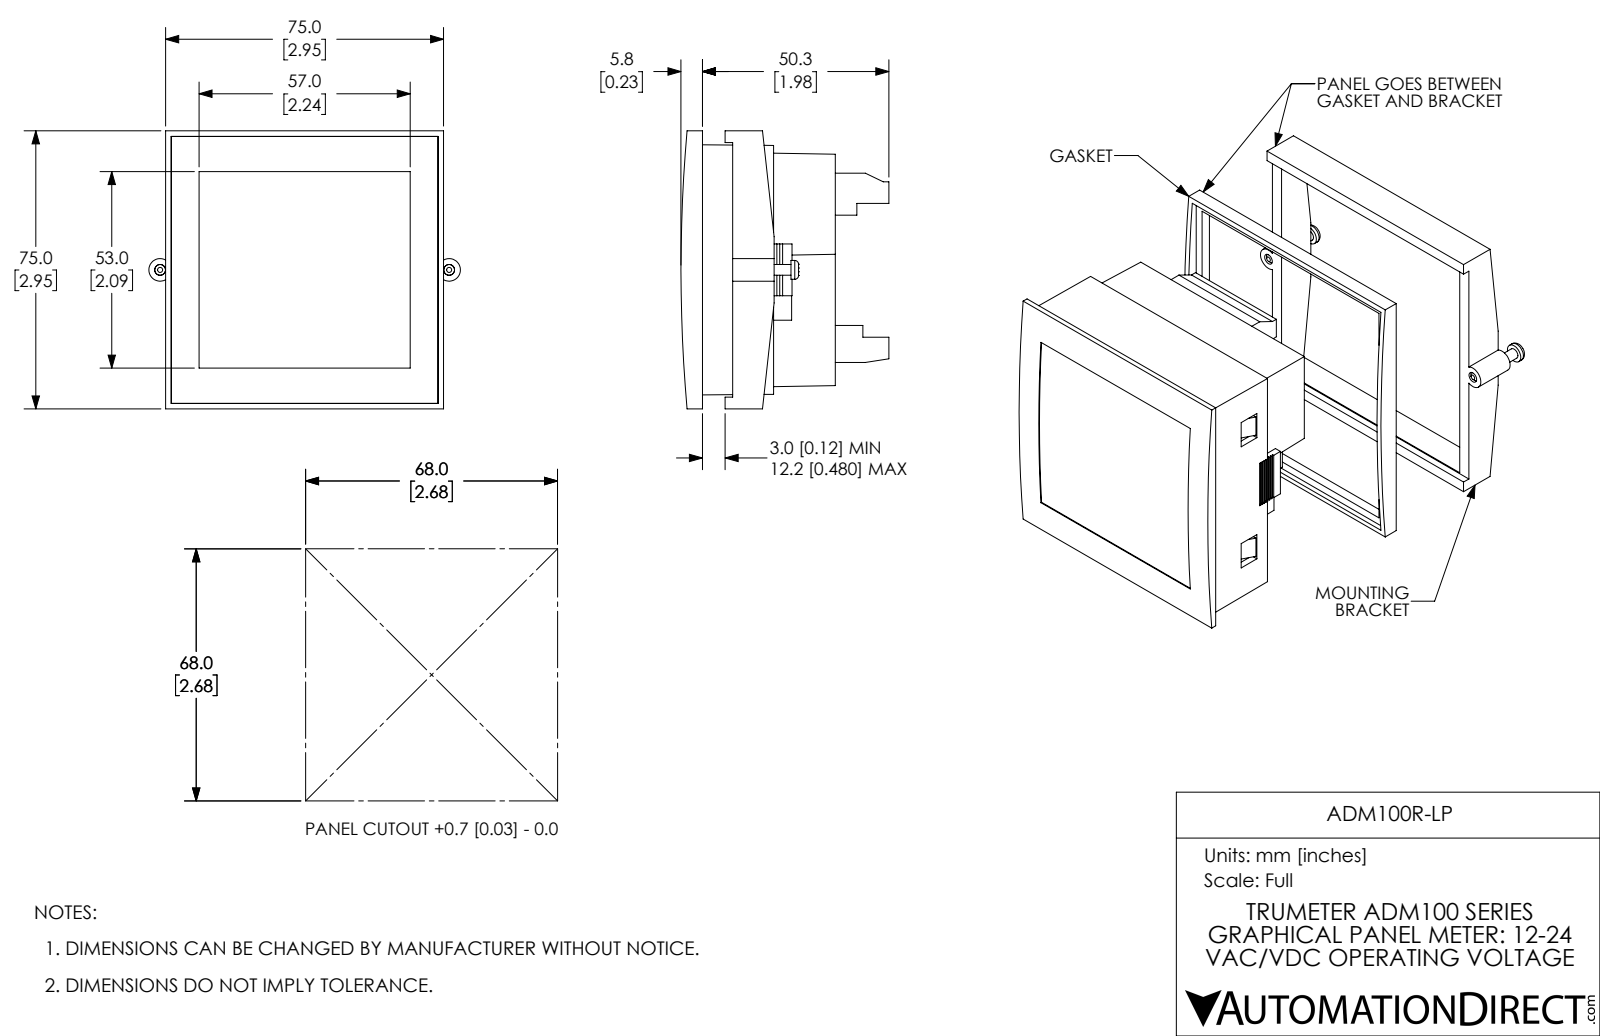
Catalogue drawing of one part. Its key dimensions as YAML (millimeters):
part_name: "ADM100R-LP"
step_written_by: "SolidWorks 2021 (CONFIG_CONTROL_DESIGN)"
units: millimeters
bodies: {solids: 23, faces: 419, planar: 335, cylindrical: 76, other: 8}
overall_size: [84.1, 75, 56.1]
volume: 156700
surface_area: 58480
round_holes:
  - {diameter: 3.8, count: 13}
  - {diameter: 2.9, count: 2}
round_bosses_or_shafts:
  - {diameter: 3.8, count: 13}
  - {diameter: 5.1, count: 2}
  - {diameter: 2.9, count: 2}
partial_cylinders:
  - {radius: 3, count: 2}
  - {radius: 432.7, count: 2}
face_to_face_distances: [1.9, 7.7, 6, 69, 67.5, 2.3, 3.8, 71.2, 65.6, 29]
hole_center_spacings: [42, 5.1, 42.6, 10.2, 43.8, 15.2, 45.5, 20.3]
